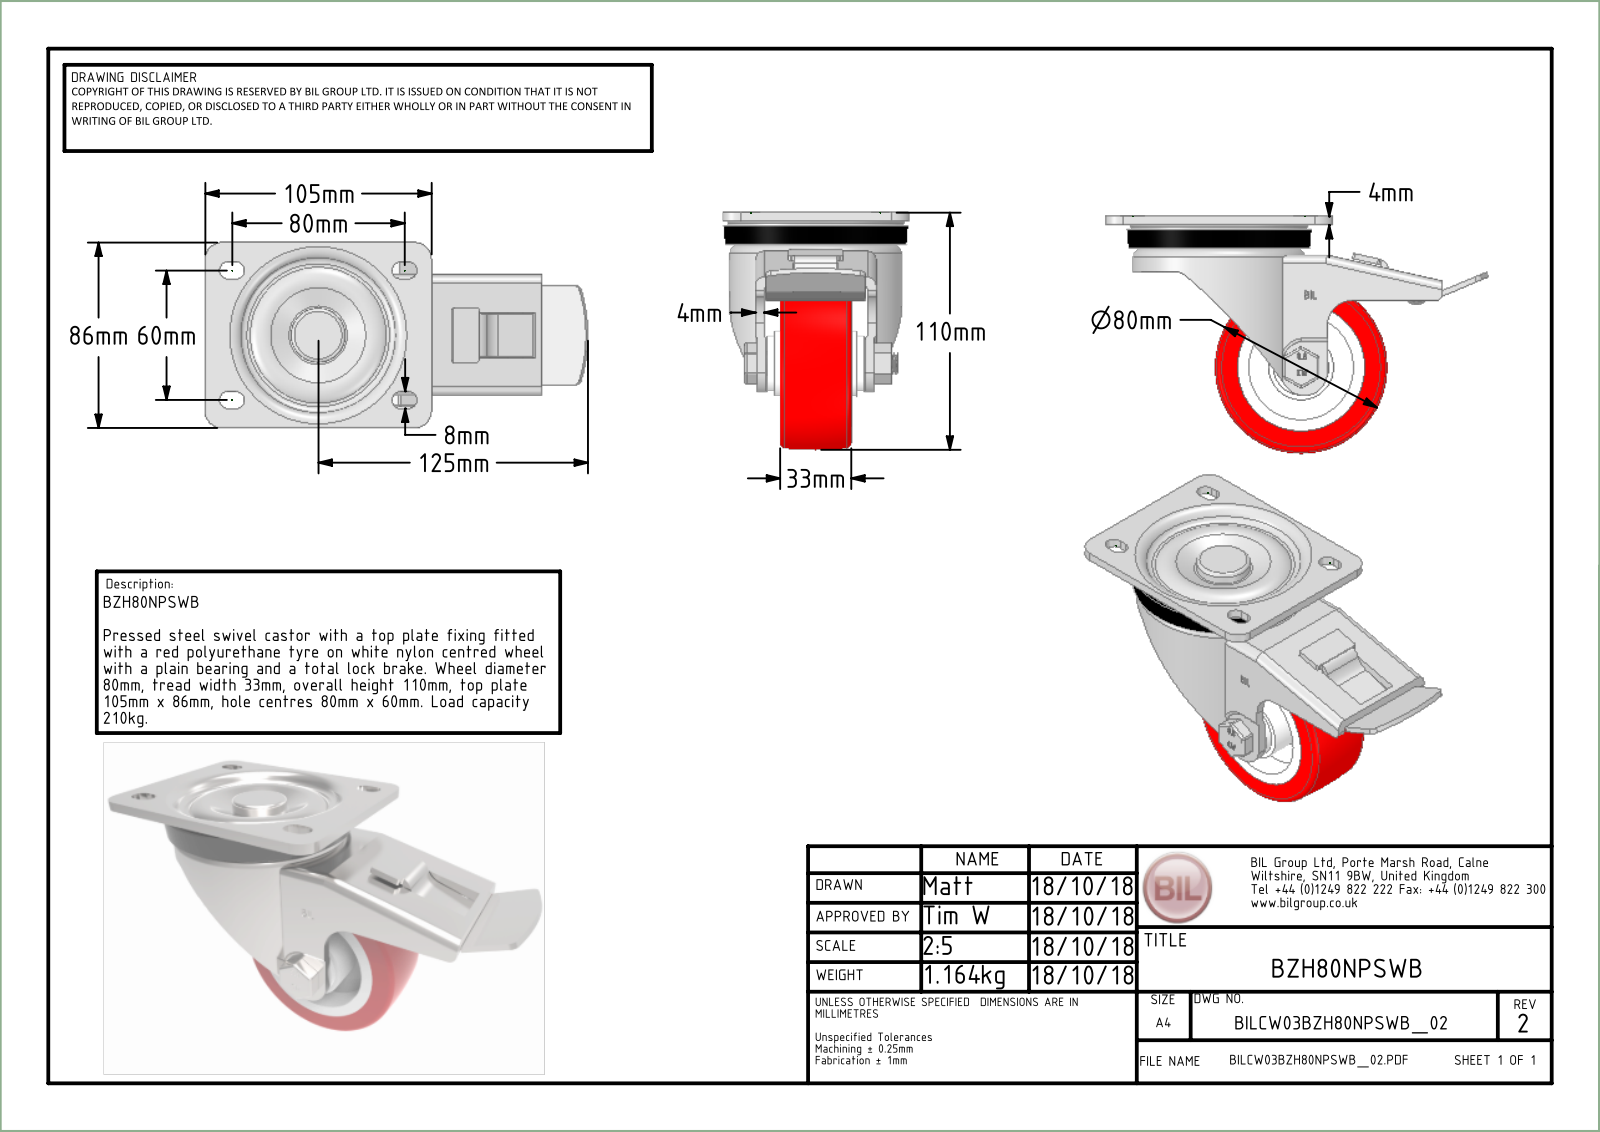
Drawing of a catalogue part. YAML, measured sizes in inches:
part_name: "BZH80NPSWB v3; BZH80ASSWB v1; ZINC PLATED, PRESSED STEEL TOP PLATE; ZINC PLATED, PRESSED STEEL FORKS (+8 more)"
step_written_by: "Autodesk Translation Framework v14.10.0.0 (AUTOMOTIVE_DESIGN)"
units: inches
bodies: {solids: 12, faces: 586, planar: 310, cylindrical: 174, other: 102}
overall_size: [6.909, 4.331, 3.386]
volume: 17.94
surface_area: 196
round_holes:
  - {diameter: 0.315, count: 1}
  - {diameter: 0.394, count: 1}
  - {diameter: 0.402, count: 1}
  - {diameter: 0.472, count: 1}
  - {diameter: 0.492, count: 1}
  - {diameter: 0.984, count: 1}
  - {diameter: 1.26, count: 1}
  - {diameter: 2.283, count: 1}
  - {diameter: 2.835, count: 1}
round_bosses_or_shafts:
  - {diameter: 3.15, count: 1}
  - {diameter: 2.323, count: 1}
  - {diameter: 1.22, count: 1}
  - {diameter: 1.024, count: 1}
  - {diameter: 0.787, count: 1}
  - {diameter: 0.63, count: 1}
  - {diameter: 0.47, count: 1}
  - {diameter: 0.388, count: 1}
partial_cylinders:
  - {radius: 0.02, count: 18}
  - {radius: 0.03, count: 12}
  - {radius: 0.079, count: 10}
  - {radius: 0.177, count: 8}
  - {radius: 0.157, count: 5}
  - {radius: 0.098, count: 4}
  - {radius: 0.118, count: 4}
  - {radius: 0.315, count: 4}
face_to_face_distances: [0.157, 0.413, 0.295, 0.256, 0.039, 0.453, 0.02, 0.138, 1.713, 0.177]
